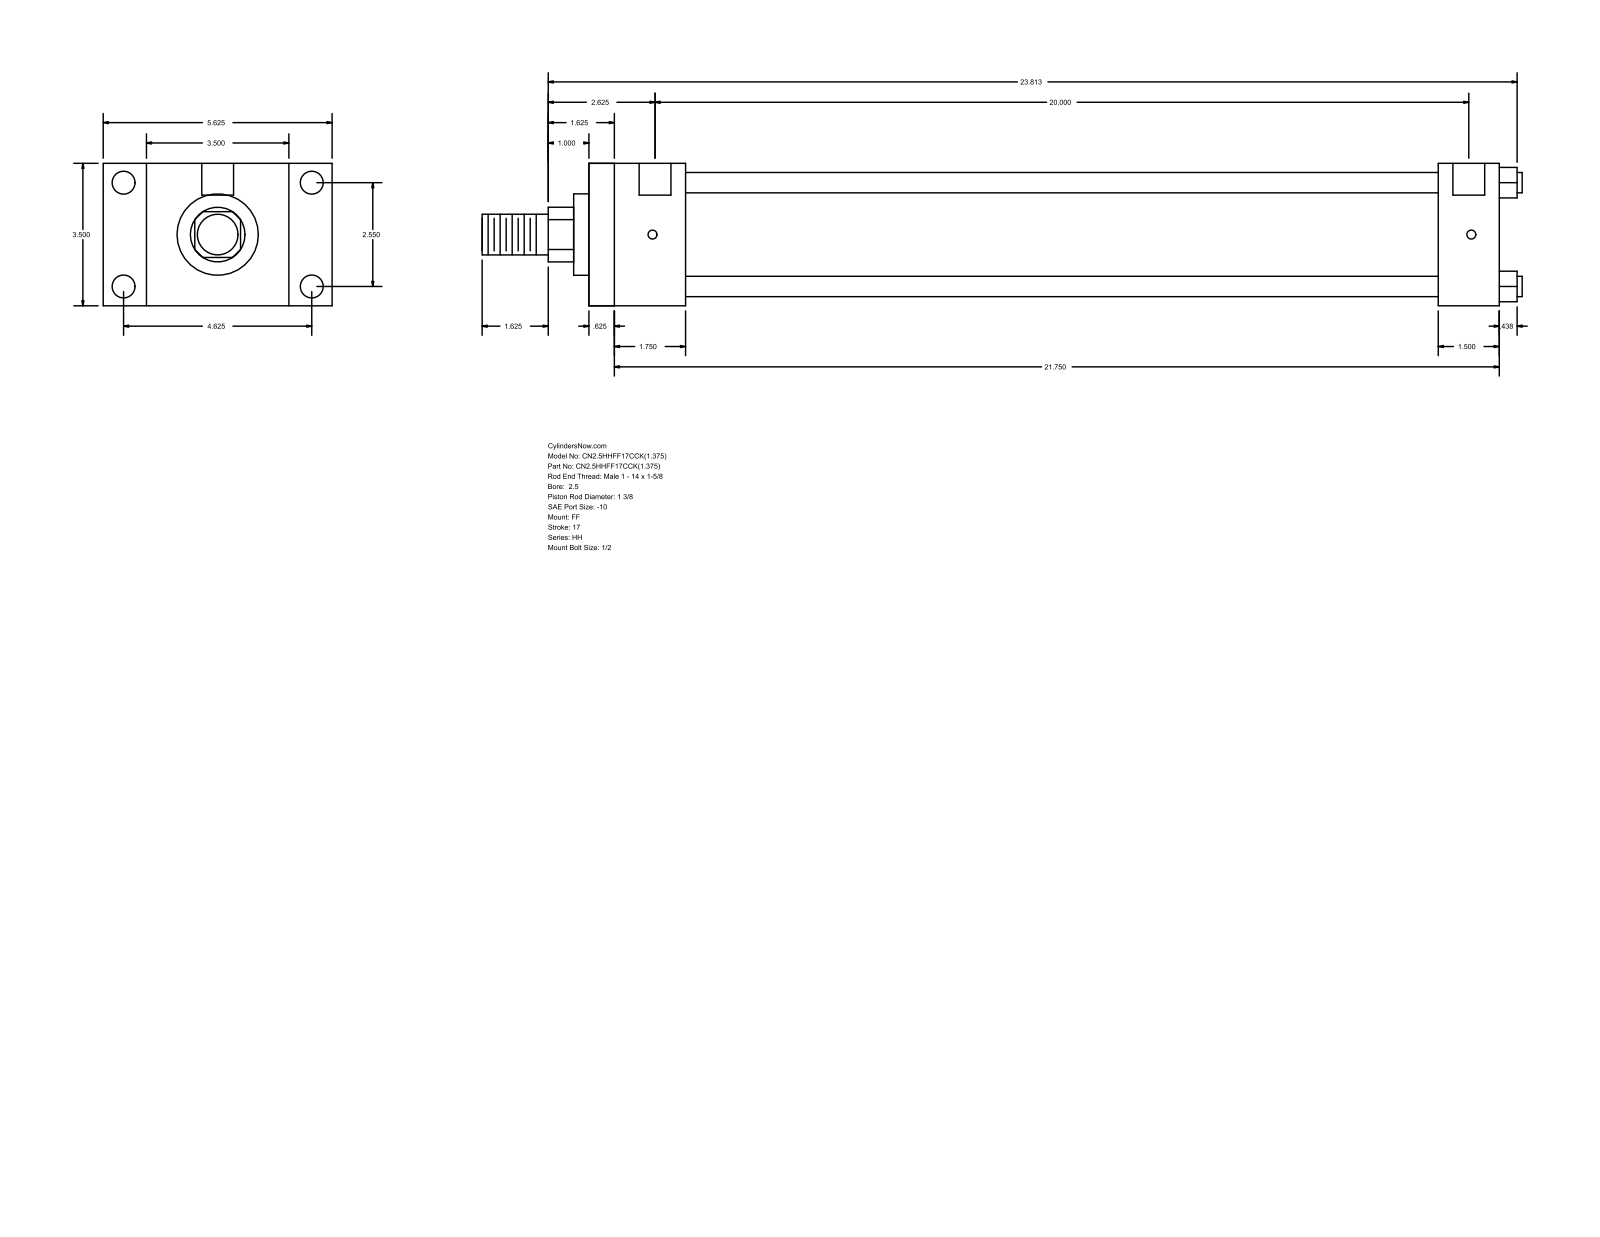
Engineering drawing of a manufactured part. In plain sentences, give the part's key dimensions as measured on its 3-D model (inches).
The part is named "HH_FF__0250_1.375". Its 3-D file was written by "GSSL Pune (CONFIG_CONTROL_DESIGN)". It is 0 solids with 92 faces: 64 planar, 28 cylindrical and 0 other. Overall it measures 25.563 by 5.625 by 3.5 inches. Round holes: 4 of diameter 0.219, 4 of diameter 0.563, 2 of diameter 0.781. Round bosses or shafts: 4 of diameter 0.5, 1 of diameter 2.875, 1 of diameter 2, 1 of diameter 1.375, 1 of diameter 1. Partial cylindrical surfaces (rounded edges, fillets, slot ends): 1 of radius 0.672. The main face-to-face distances are 3.5, 22.375, 0.625, 21.75, 2.375, 1.75, 20, 20.875, 20.25, 18.5. The hole center spacings are 2.55, 4.625, 5.281, 20.125, 0.062, 0.063, 20, 20.062.
